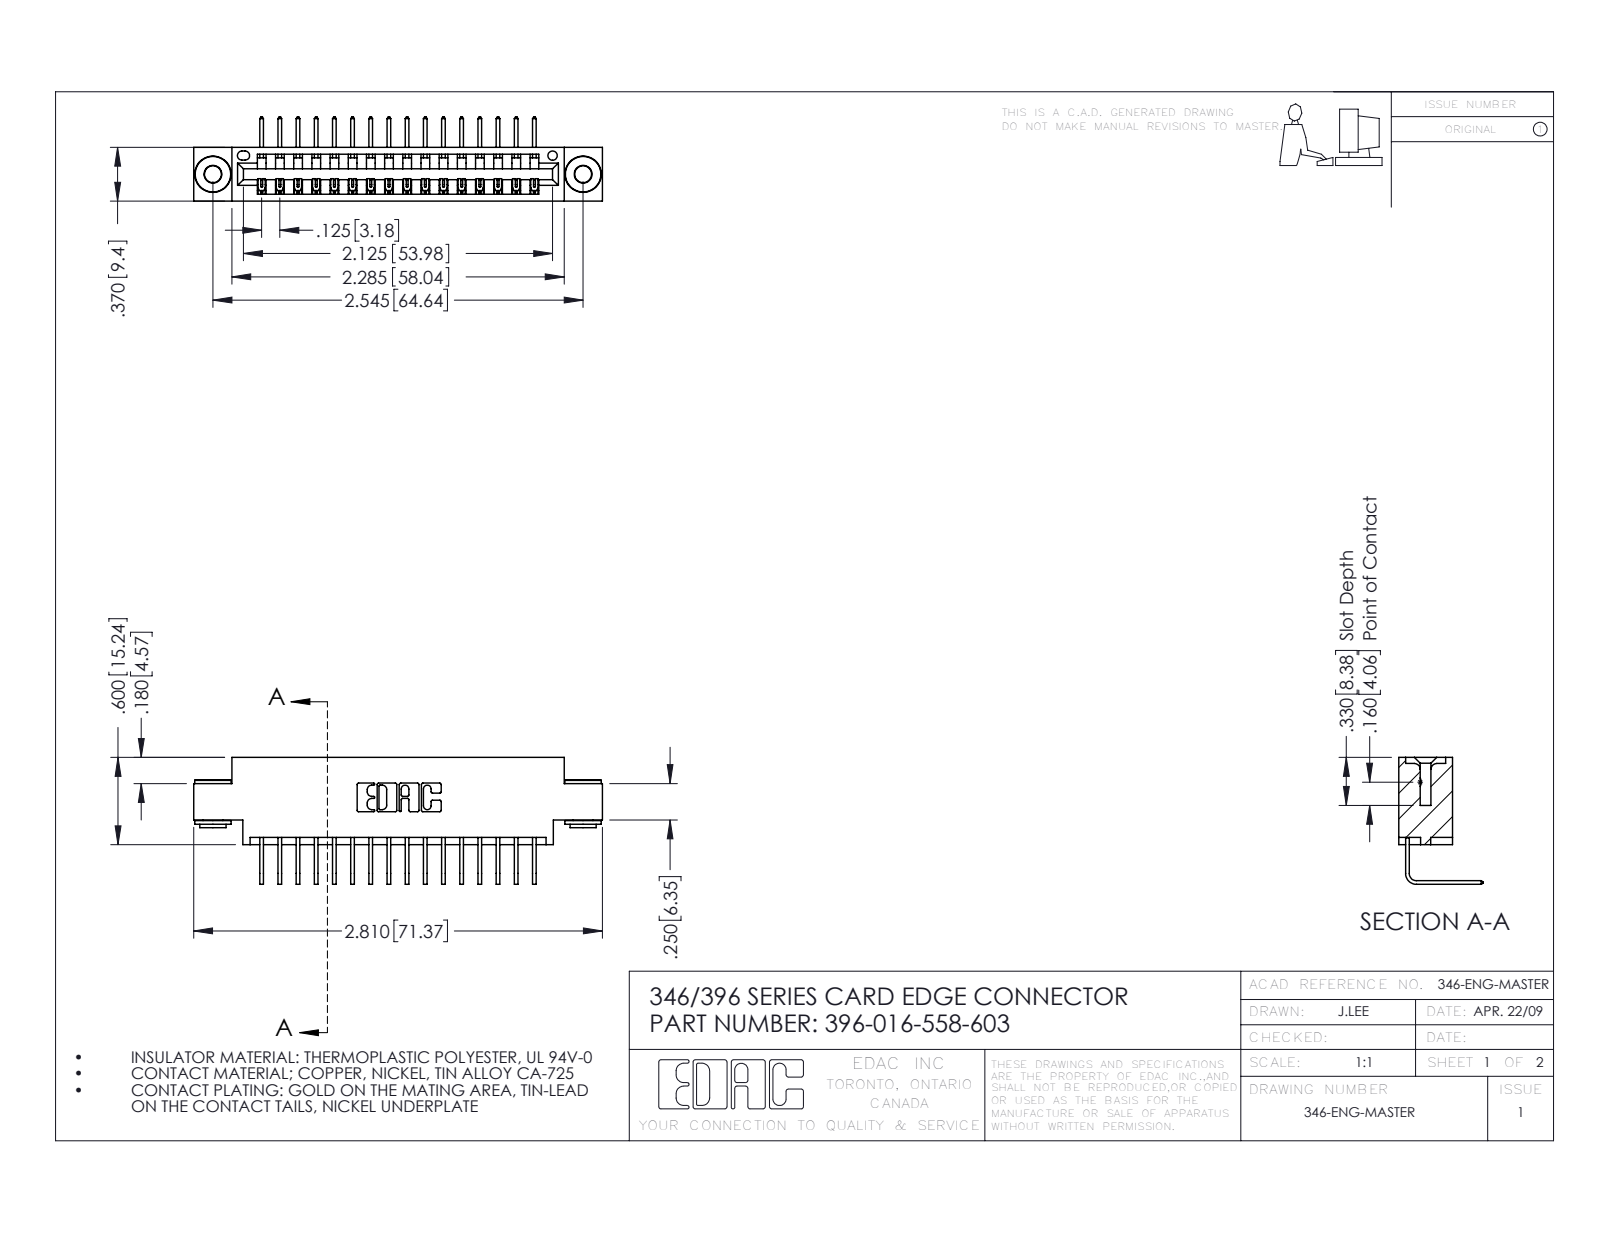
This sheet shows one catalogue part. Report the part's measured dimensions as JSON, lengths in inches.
{"part_name": "345-292-001_558 Tail - 2; 396-016-558-603; 345-250-002_345-250-002-102; 346 Part_0.170 Offset - 0.156 Dia-TH", "step_written_by": "SolidWorks 2016 (CONFIG_CONTROL_DESIGN)", "units": "inches", "bodies": {"solids": 19, "faces": 1124, "planar": 762, "cylindrical": 354, "other": 8}, "overall_size": [2.81, 0.873, 0.58], "volume_in3": 0.401, "surface_area_in2": 13.38, "round_holes": [[0.116, 2], [0.156, 2], [0.064, 1]], "round_bosses_or_shafts": [[0.25, 2], [0.18, 2], [0.136, 2]], "partial_cylinders_radius": [[0.006, 32], [0.01, 22], [0.007, 6], [0.031, 6], [0.026, 3], [0.031, 2], [0.04, 2], [0.014, 1]], "face_to_face_distances": [0.322, 0.37, 0.048, 0.25, 0.025, 0.298, 0.072, 0.148, 0.222, 0.1], "hole_center_spacings": [0.246, 2.338, 2.545]}
